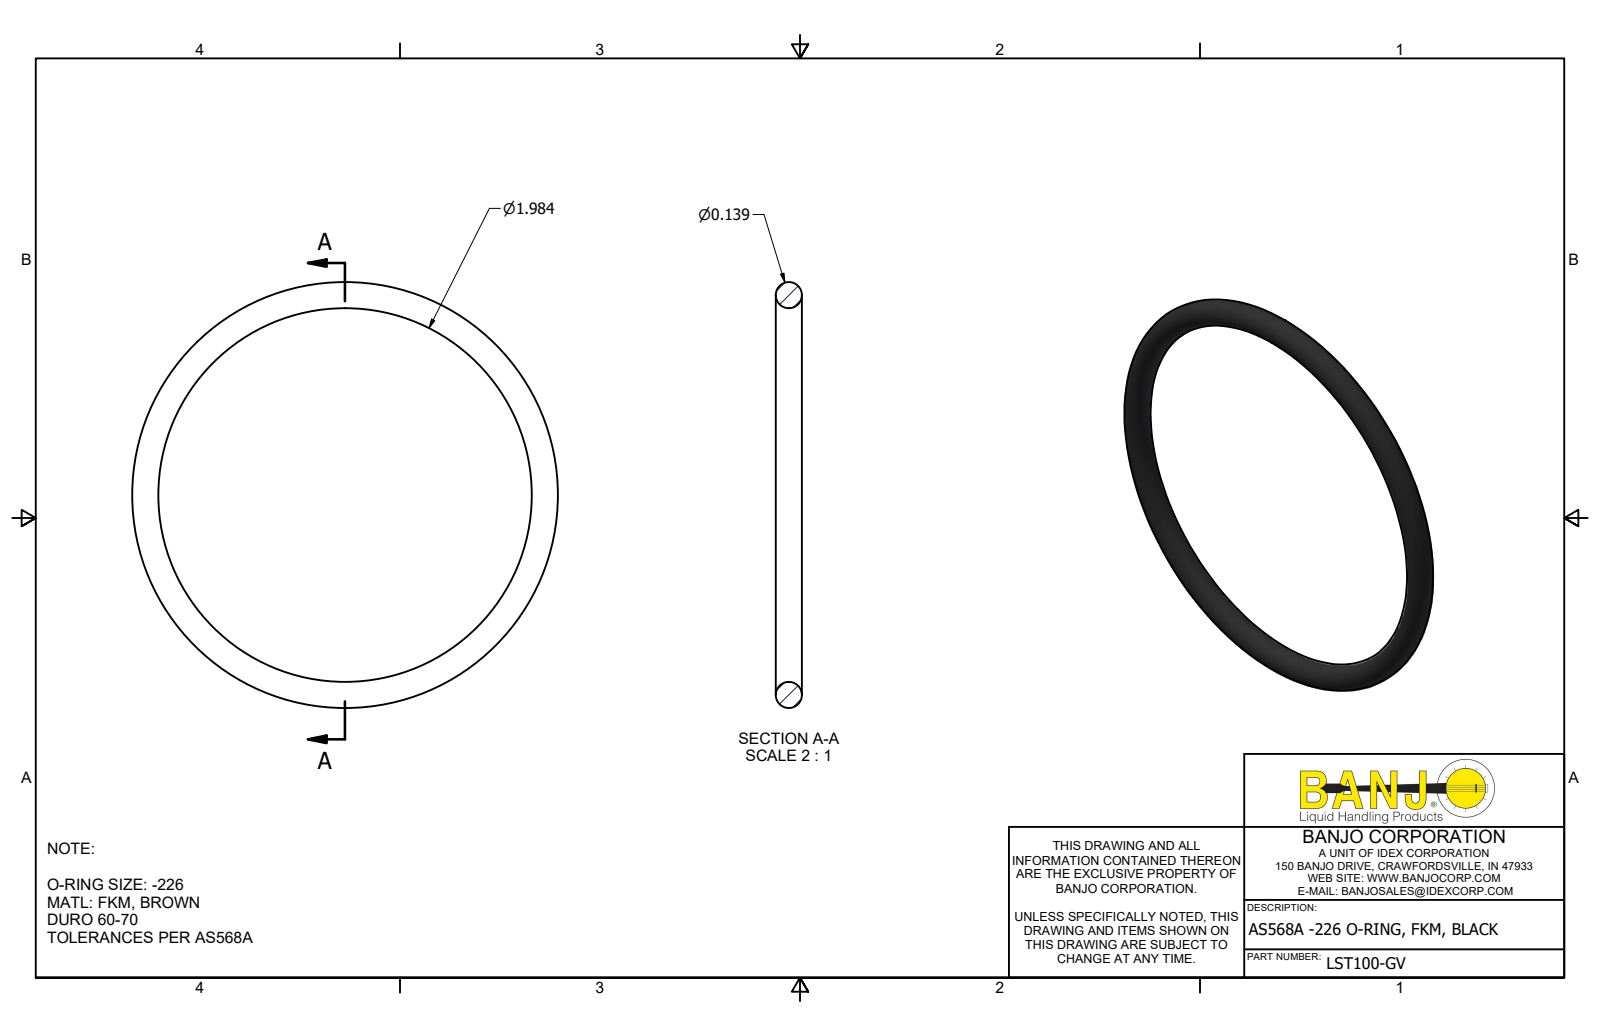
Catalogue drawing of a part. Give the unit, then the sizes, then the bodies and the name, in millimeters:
Units: millimetres
Overall size (bounding box): 57.5 × 57.5 × 3.5
Volume: 1 660 mm³ · Surface area: 1 879 mm²
Bodies: 1 solid, 1 faces (0 planar, 0 cylindrical, 1 other)
Part name (STEP PRODUCT): LST100-GV
STEP written by: Autodesk Inventor 2022 (AUTOMOTIVE_DESIGN)
